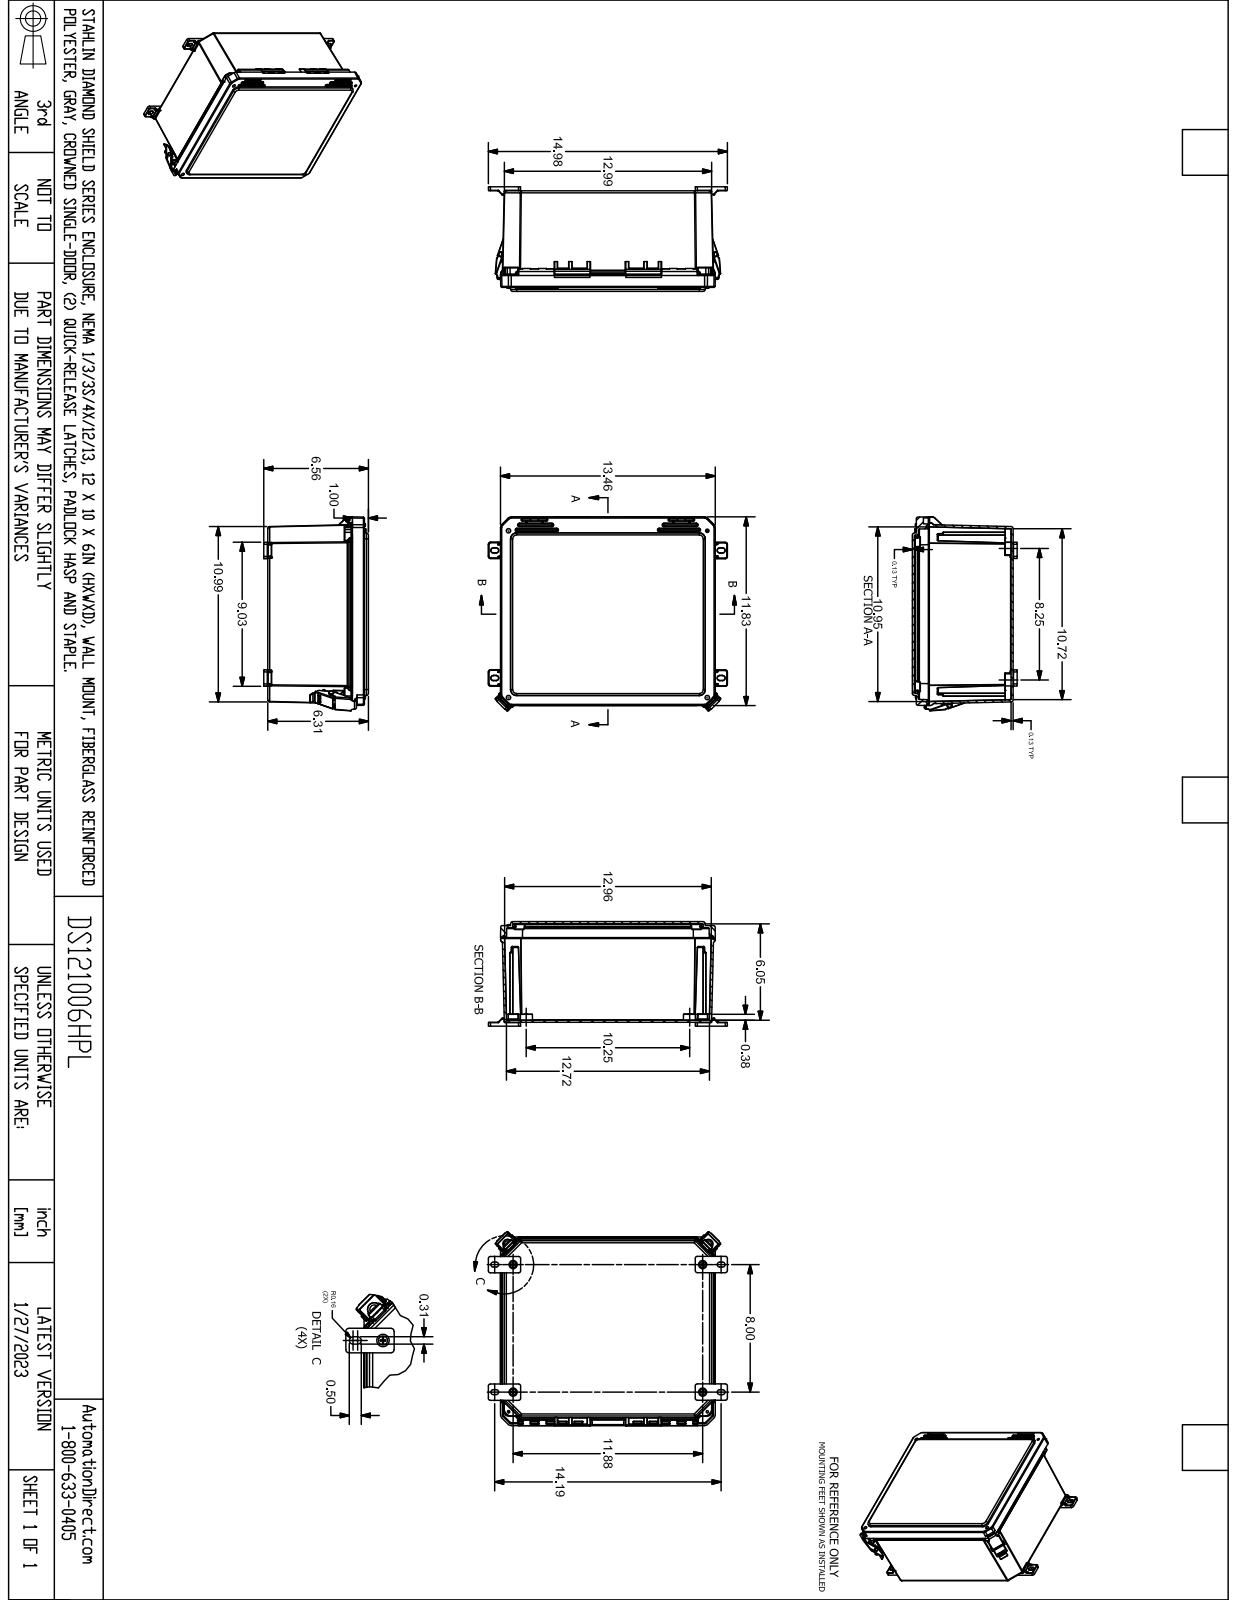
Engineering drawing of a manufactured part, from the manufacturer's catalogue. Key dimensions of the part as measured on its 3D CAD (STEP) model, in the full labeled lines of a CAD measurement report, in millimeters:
Part name (STEP PRODUCT): FR121006HPL
STEP written by: SolidWorks 2021 (AUTOMOTIVE_DESIGN)
Units: millimetres
Bodies: 29 solids, 2393 faces (757 planar, 1028 cylindrical, 608 other)
Overall size (bounding box): 358.6 × 308.9 × 169.4
Volume: 1 534 000 mm³ · Surface area: 834 800 mm²
Round holes (diameter × count): ⌀3.4 ×8, ⌀3.9 ×8, ⌀4 ×8, ⌀3.4 ×4, ⌀3.8 ×4, ⌀4 ×4, ⌀6.4 ×4, ⌀6.4 ×4, ⌀3.5 ×3, ⌀5.6 ×2, ⌀5.8 ×2, ⌀8 ×2
Round bosses / shafts (diameter × count): ⌀6.9 ×8, ⌀22.1 ×4, ⌀7.6 ×4, ⌀6.7 ×4, ⌀5.3 ×4, ⌀3.4 ×3, ⌀11 ×1, ⌀11 ×1
Partial cylindrical surfaces — rounded edges, fillets, slot ends (radius × count): R0.3 ×174, R0.1 ×94, R0.8 ×71, R0.5 ×70, R1.5 ×36, R2.3 ×26, R0.8 ×24, R2.4 ×24
Main face-to-face distances: 3.2, 157, 160.2, 153.9, 3.6, 3.5, 3.6, 6.4, 3.5, 150.7
Hole centre spacings: 316.3, 316.4, 310.6, 289.7, 299.9, 373.6, 6.4, 239.2
